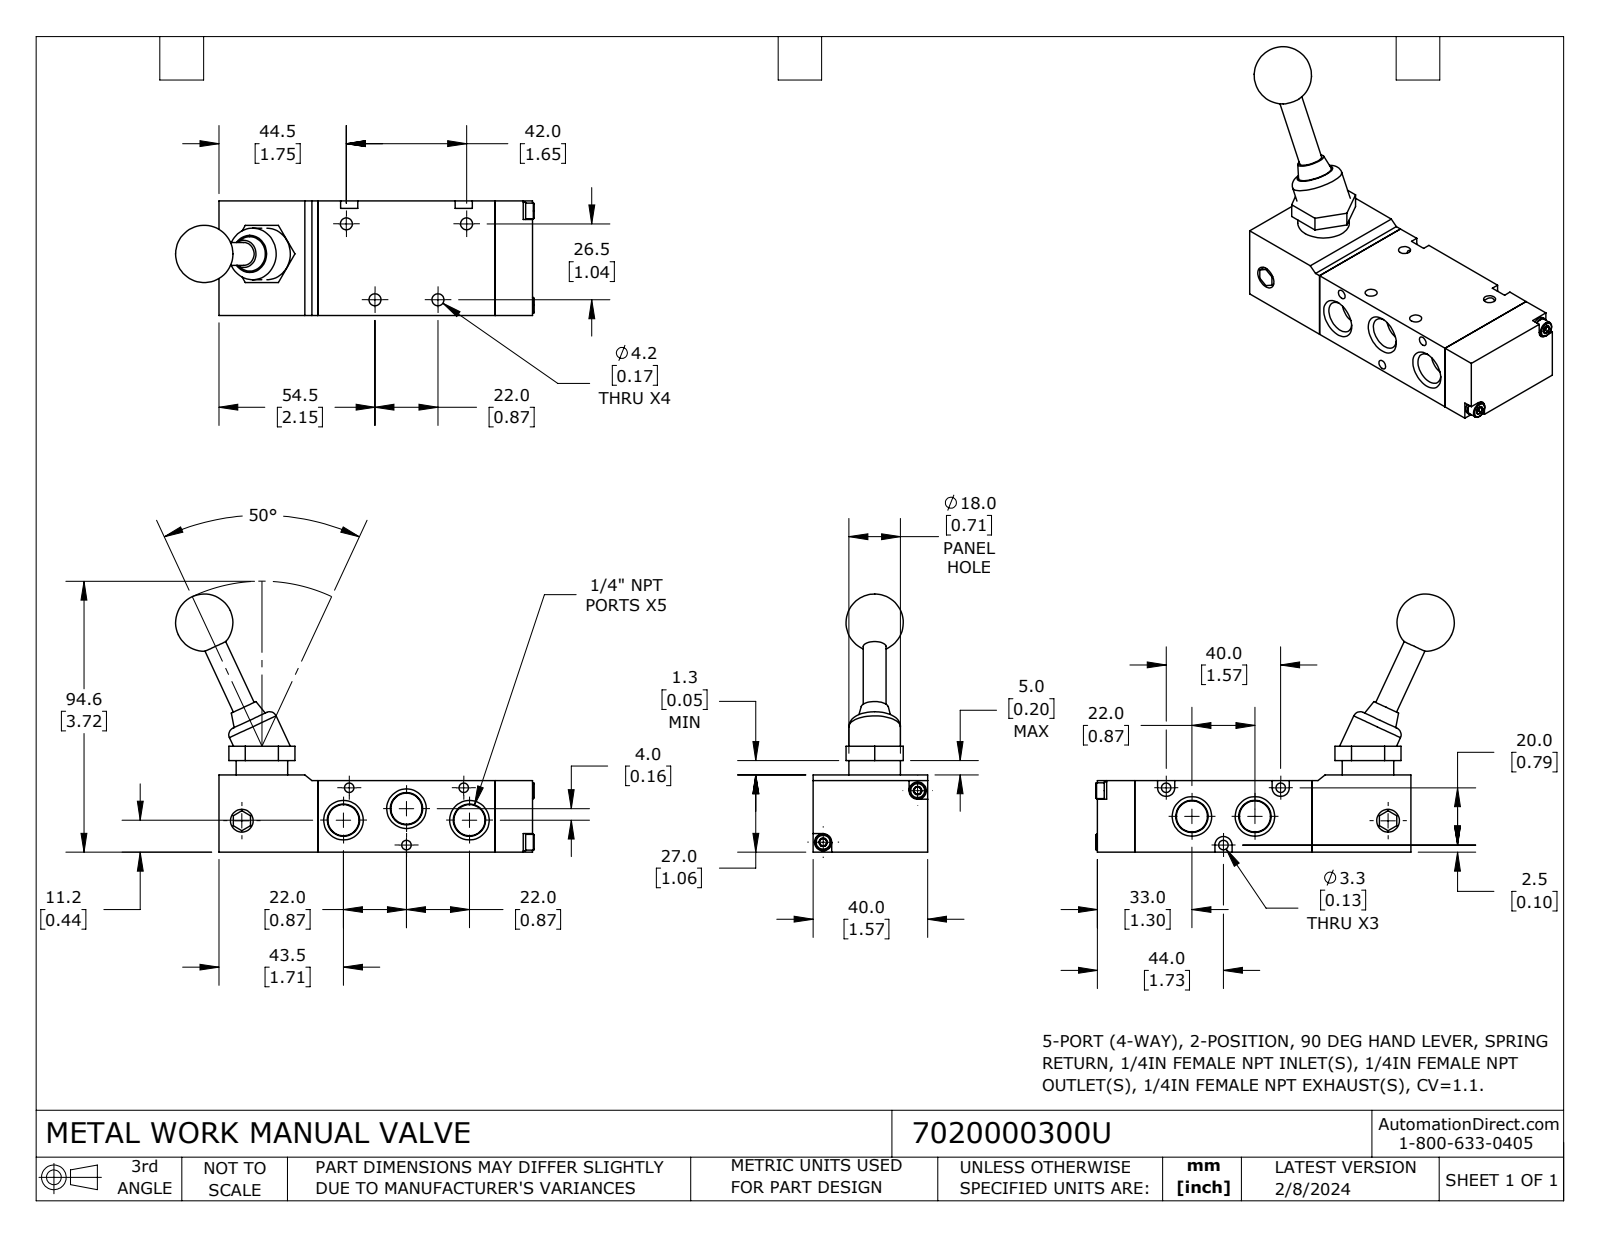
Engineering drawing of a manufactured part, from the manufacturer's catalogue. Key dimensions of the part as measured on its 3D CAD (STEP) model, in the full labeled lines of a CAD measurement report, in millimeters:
Part name (STEP PRODUCT): 7020000300U
STEP written by: SolidWorks 2023 (CONFIG_CONTROL_DESIGN)
Units: millimetres
Bodies: 8 solids, 206 faces (101 planar, 51 cylindrical, 54 other)
Overall size (bounding box): 125.2 × 90.1 × 40
Volume: 117 900 mm³ · Surface area: 28 730 mm²
Round holes (diameter × count): ⌀4.2 ×4, ⌀3.3 ×3, ⌀3 ×2, ⌀8 ×1
Round bosses / shafts (diameter × count): ⌀18 ×2, ⌀6 ×2, ⌀5.5 ×2, ⌀8 ×1
Partial cylindrical surfaces — rounded edges, fillets, slot ends (radius × count): R3 ×3
Main face-to-face distances: 25, 40, 62, 96.5, 34.5, 27, 2, 13, 75, 109.5
Hole centre spacings: 28.3, 28.3, 41.6, 22, 37.6, 39.2, 40, 42
